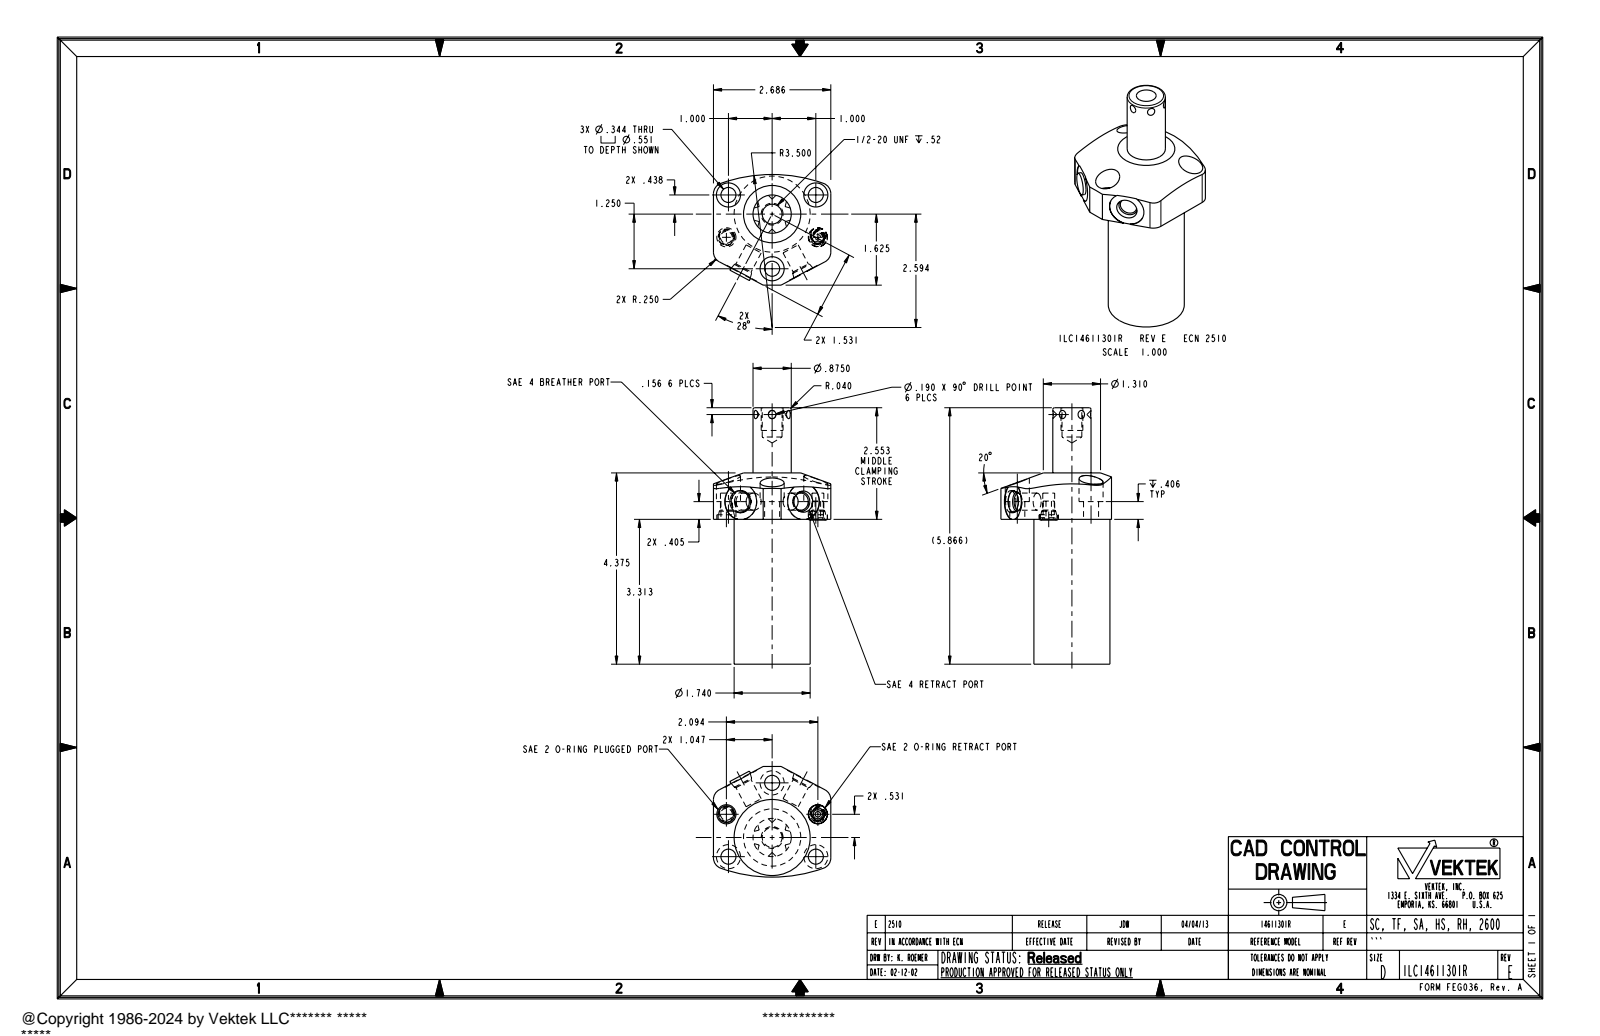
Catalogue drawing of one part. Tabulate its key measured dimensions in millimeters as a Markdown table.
| quantity | value |
| --- | --- |
| part name | ILC14611301R |
| STEP written by | PRO/ENGINEER BY PARAMETRIC TECHNOLOGY CORPORATION, 2007460 (AUTOMOTIVE_DESIGN_CC2) |
| units | millimeters |
| bodies | 1 solid, 123 faces (32 planar, 53 cylindrical, 38 other) |
| overall size | 149 × 68.2 × 64.3 |
| volume | 220 700 mm³ |
| surface area | 32 610 mm² |
| round holes (diameter × count) | 8.7 × 3, 14 × 3, 6.9 × 2, 10 × 2, 11.1 × 2, 3.2 × 1, 11.5 × 1 |
| round bosses / shafts (diameter × count) | 44.2 × 1, 22.2 × 1, 12.9 × 1, 12.7 × 1, 10.9 × 1, 9.6 × 1, 6.5 × 1, 5.3 × 1 |
| partial cylindrical surfaces (radius × count) | 6.4 × 4, 10.5 × 2, 88.9 × 1 |
| main face-to-face distances | 84.2, 68.2, 111.1, 27, 94.5, 10.3, 16.7, 149, 64.8, 54.5 |
| hole center spacings | 24.6, 27.7, 29.8, 32.3, 49.8, 57.5, 31.8, 50.8 |
